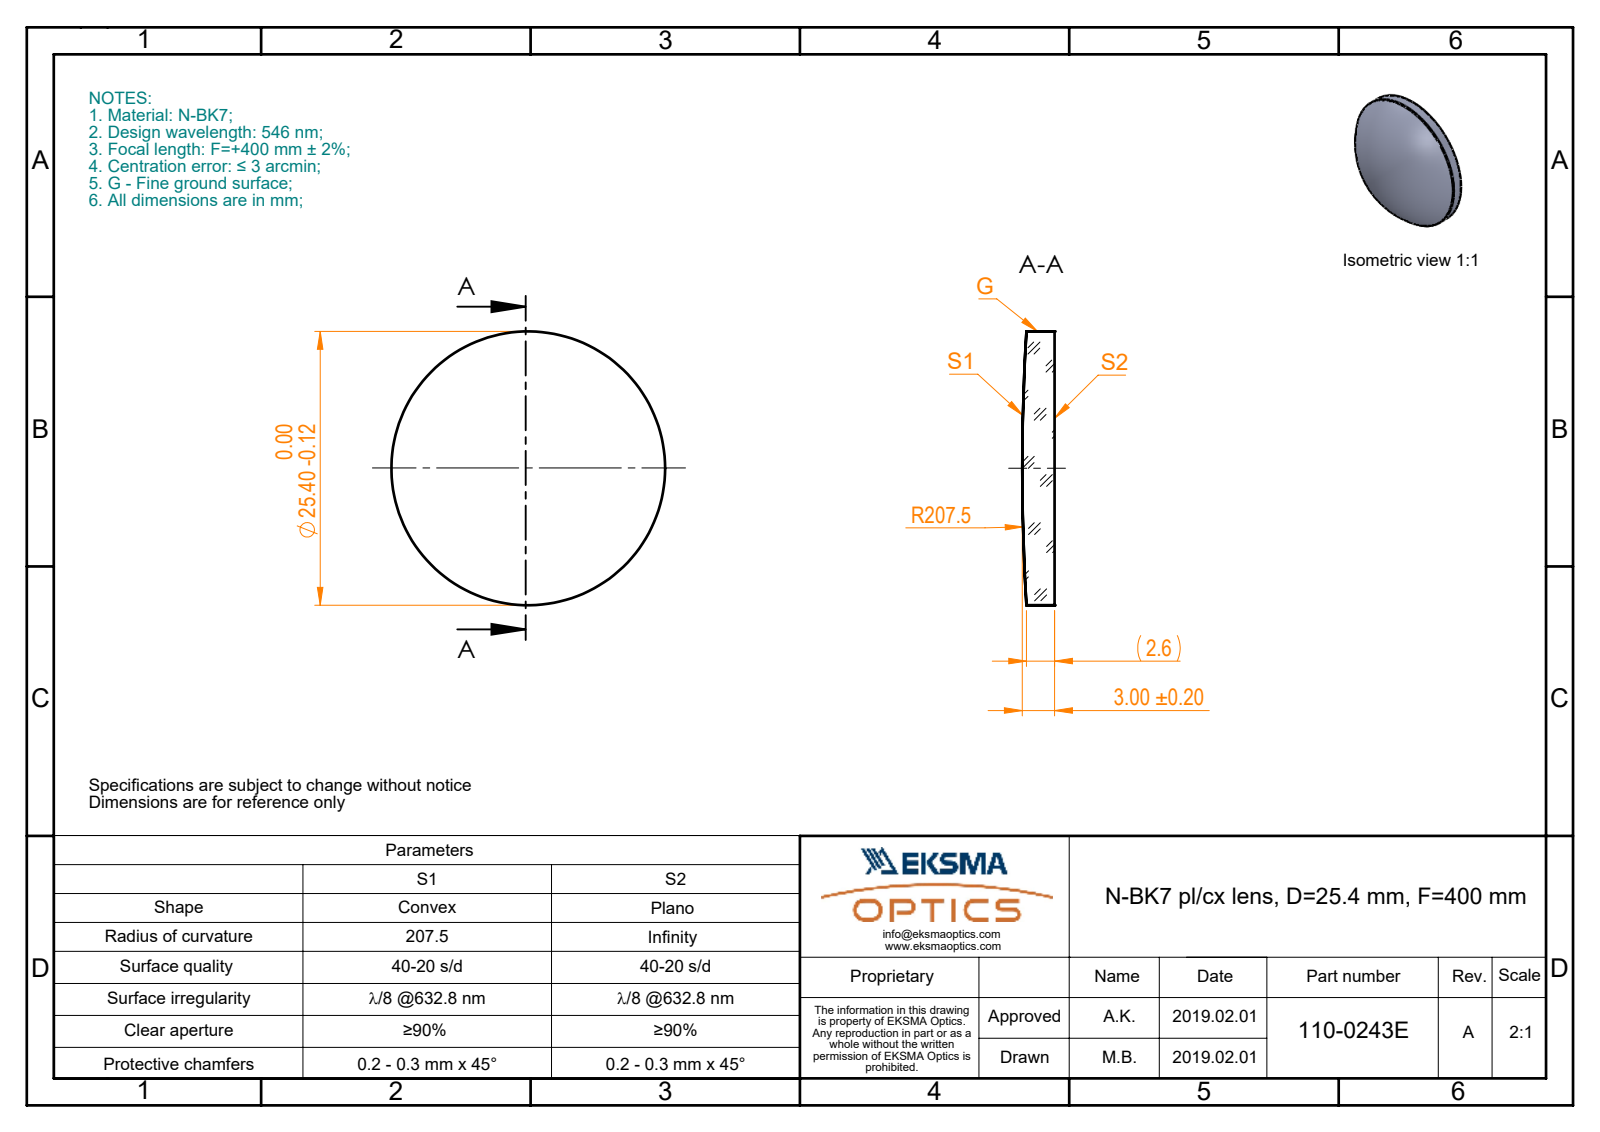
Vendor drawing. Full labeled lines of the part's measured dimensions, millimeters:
Part name (STEP PRODUCT): 110-0243E BK7 pl-cx 25.4 F400
STEP written by: SolidWorks 2017 (CONFIG_CONTROL_DESIGN)
Units: millimetres
Bodies: 1 solid, 5 faces (1 planar, 2 cylindrical, 2 other)
Overall size (bounding box): 25.4 × 25.4 × 3
Volume: 1 422 mm³ · Surface area: 1 222 mm²
Round bosses / shafts (diameter × count): ⌀25.4 ×1
